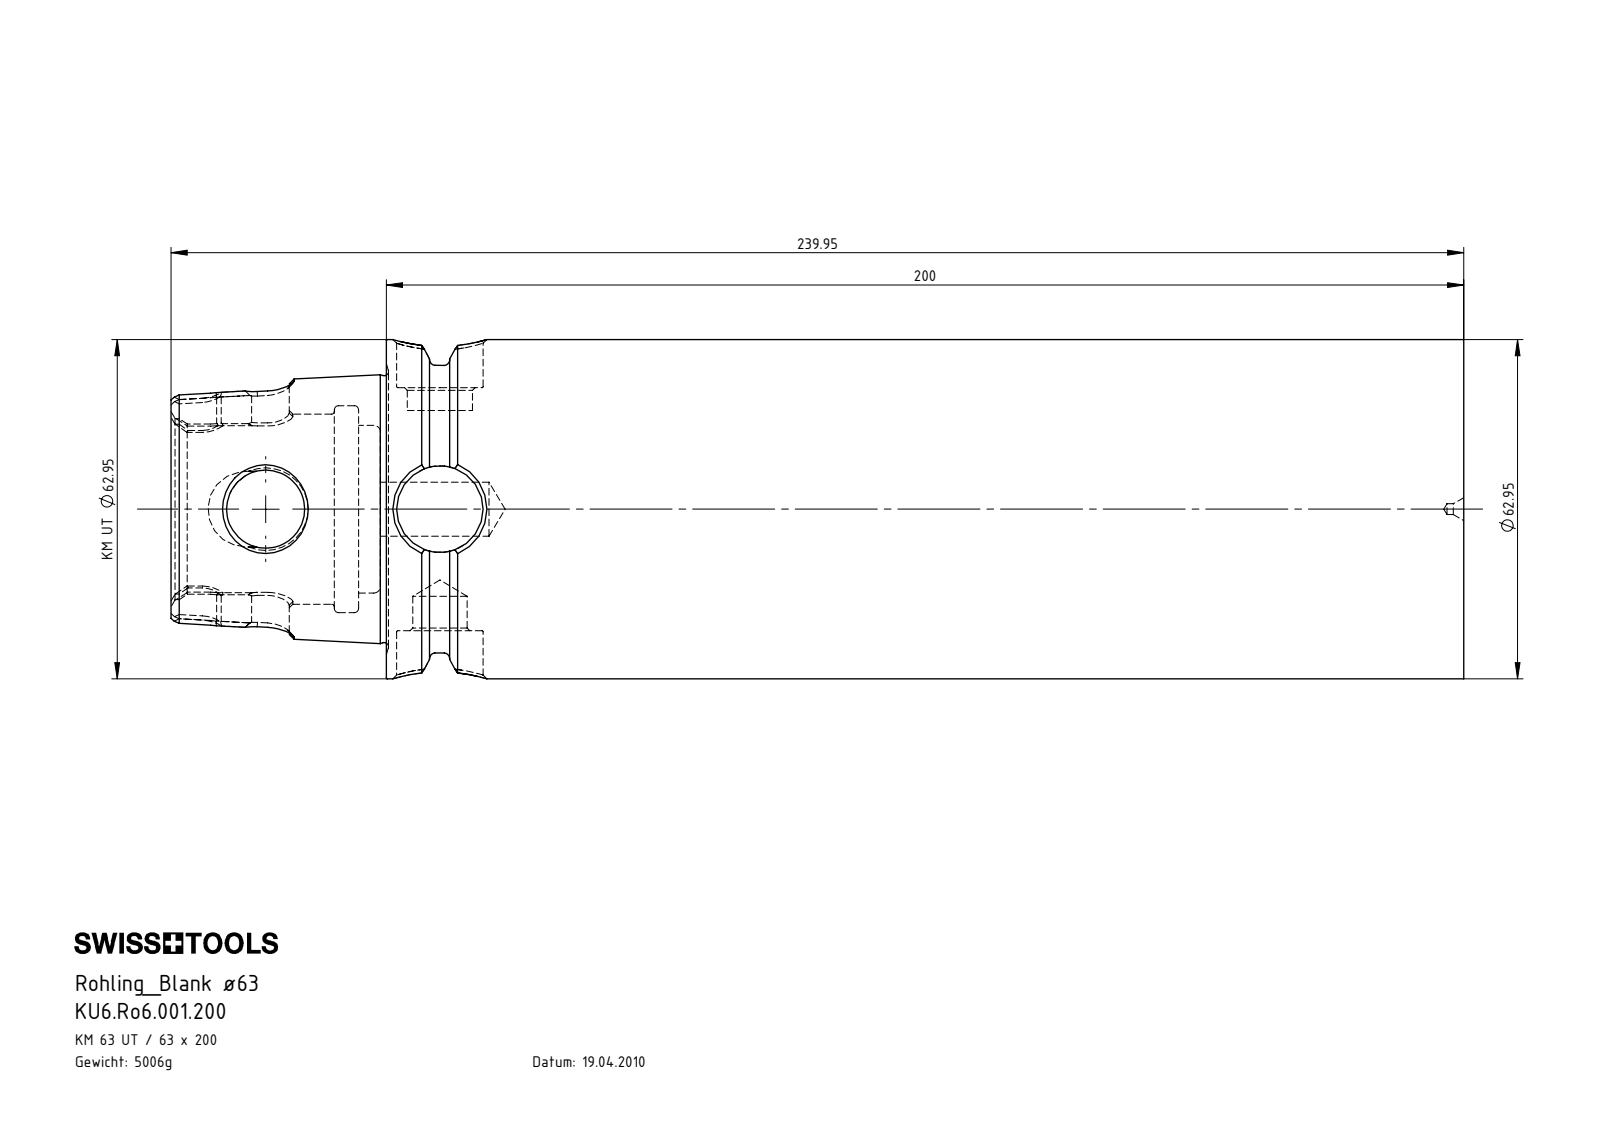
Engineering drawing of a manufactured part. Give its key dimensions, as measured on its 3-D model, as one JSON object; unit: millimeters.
{"part_name": "KU6.Ro6.001.200", "step_written_by": "SolidWorks 2017 (CONFIG_CONTROL_DESIGN)", "units": "millimeters", "bodies": {"solids": 1, "faces": 226, "planar": 50, "cylindrical": 50, "other": 126}, "overall_size": [239.95, 62.95, 62.95], "volume_mm3": 637699, "surface_area_mm2": 57494, "round_holes": [[16.05, 2], [2, 1], [10, 1], [10.1, 1], [12.1, 1], [14.5, 1], [31.1, 1], [35.27, 1], [38.4, 1]], "round_bosses_or_shafts": [[62.95, 1]], "partial_cylinders_radius": [[4, 6], [7.04, 2], [27.85, 1]], "face_to_face_distances": [200, 1.1, 201.1, 4.05, 5.15, 205.15, 45.1, 34.8, 38.85, 39.95], "hole_center_spacings": [32.35]}
